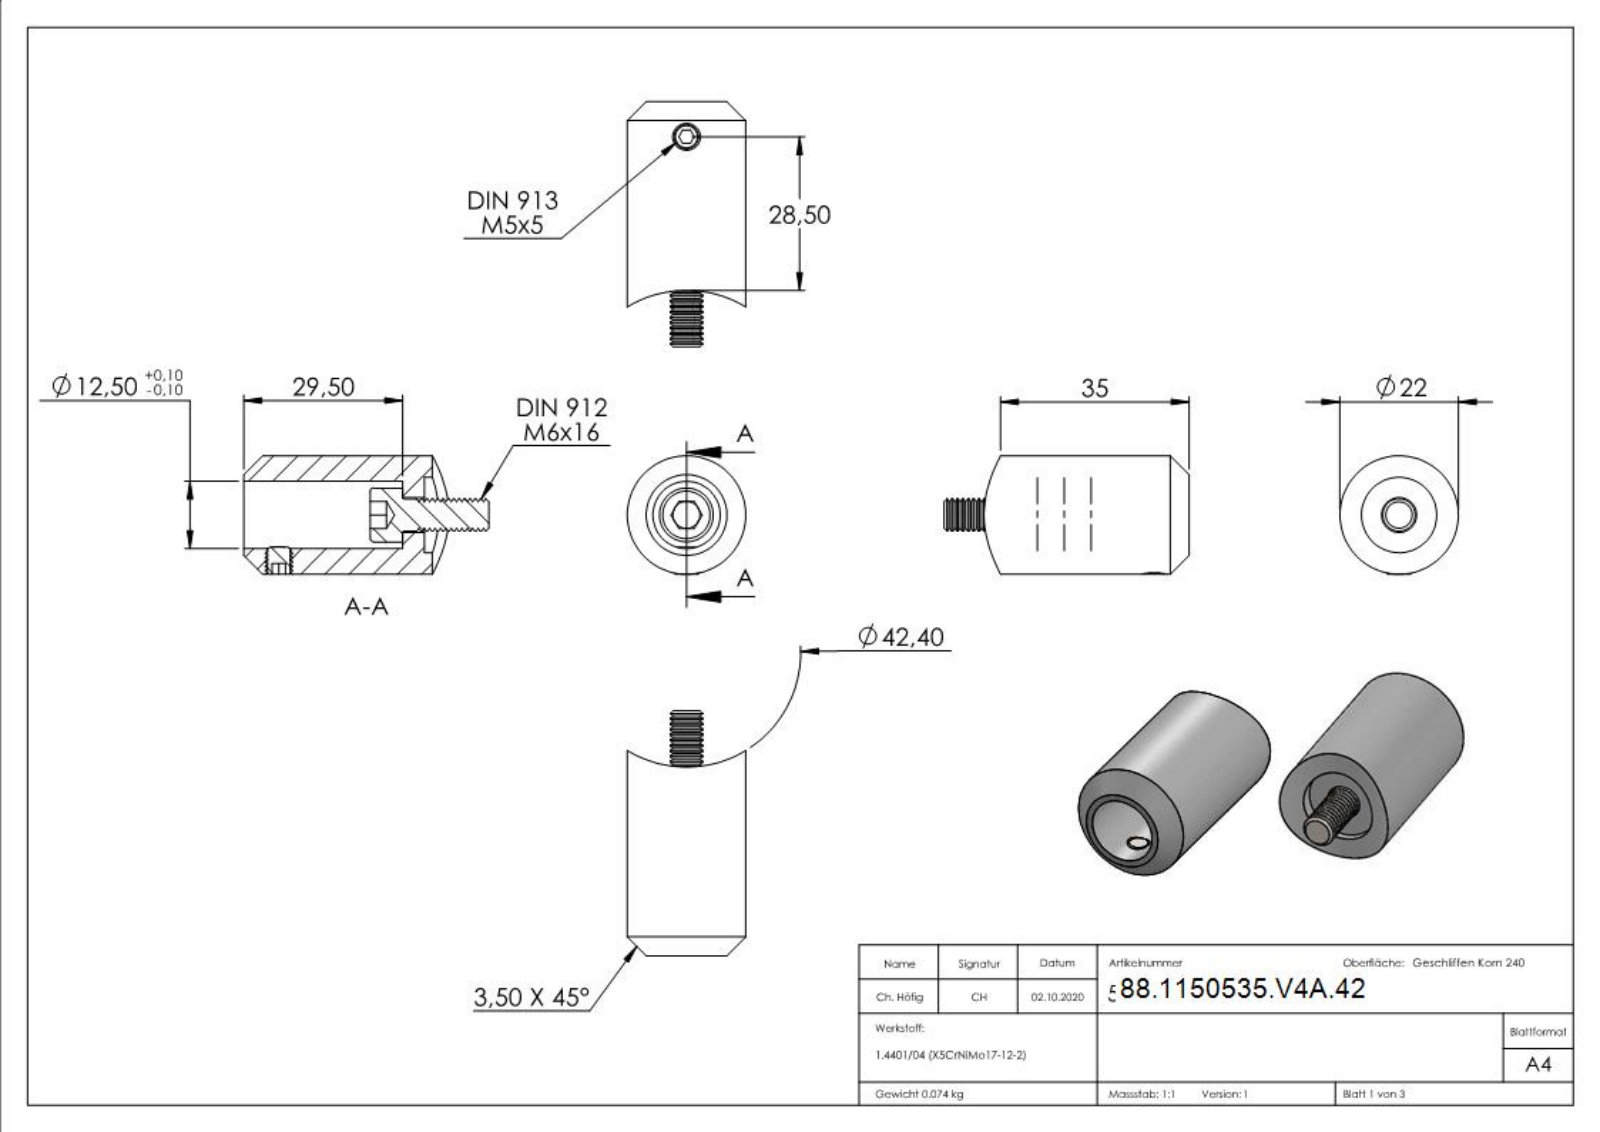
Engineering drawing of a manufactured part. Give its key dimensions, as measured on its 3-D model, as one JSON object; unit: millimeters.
{"part_name": "socket set screw flat point_din; 50535-240-XX Teil1; 50535-V4A-42; socket head cap screw_din_DIN 912 M6 x 16 --- 16S (+3 more)", "step_written_by": "SolidWorks 2018 (CONFIG_CONTROL_DESIGN)", "units": "millimeters", "bodies": {"solids": 3, "faces": 439, "planar": 180, "cylindrical": 66, "other": 193}, "overall_size": [45.5, 22, 22], "volume_mm3": 9976, "surface_area_mm2": 5396, "round_holes": [[4.2, 1], [6.5, 1], [12.5, 1], [14, 1]], "round_bosses_or_shafts": [[22, 1], [10, 1], [6, 1], [5, 1]], "partial_cylinders_radius": [[21.2, 1]], "face_to_face_distances": [4, 33.5, 29.5, 6, 10, 23.5, 5.02, 12, 16, 22]}
